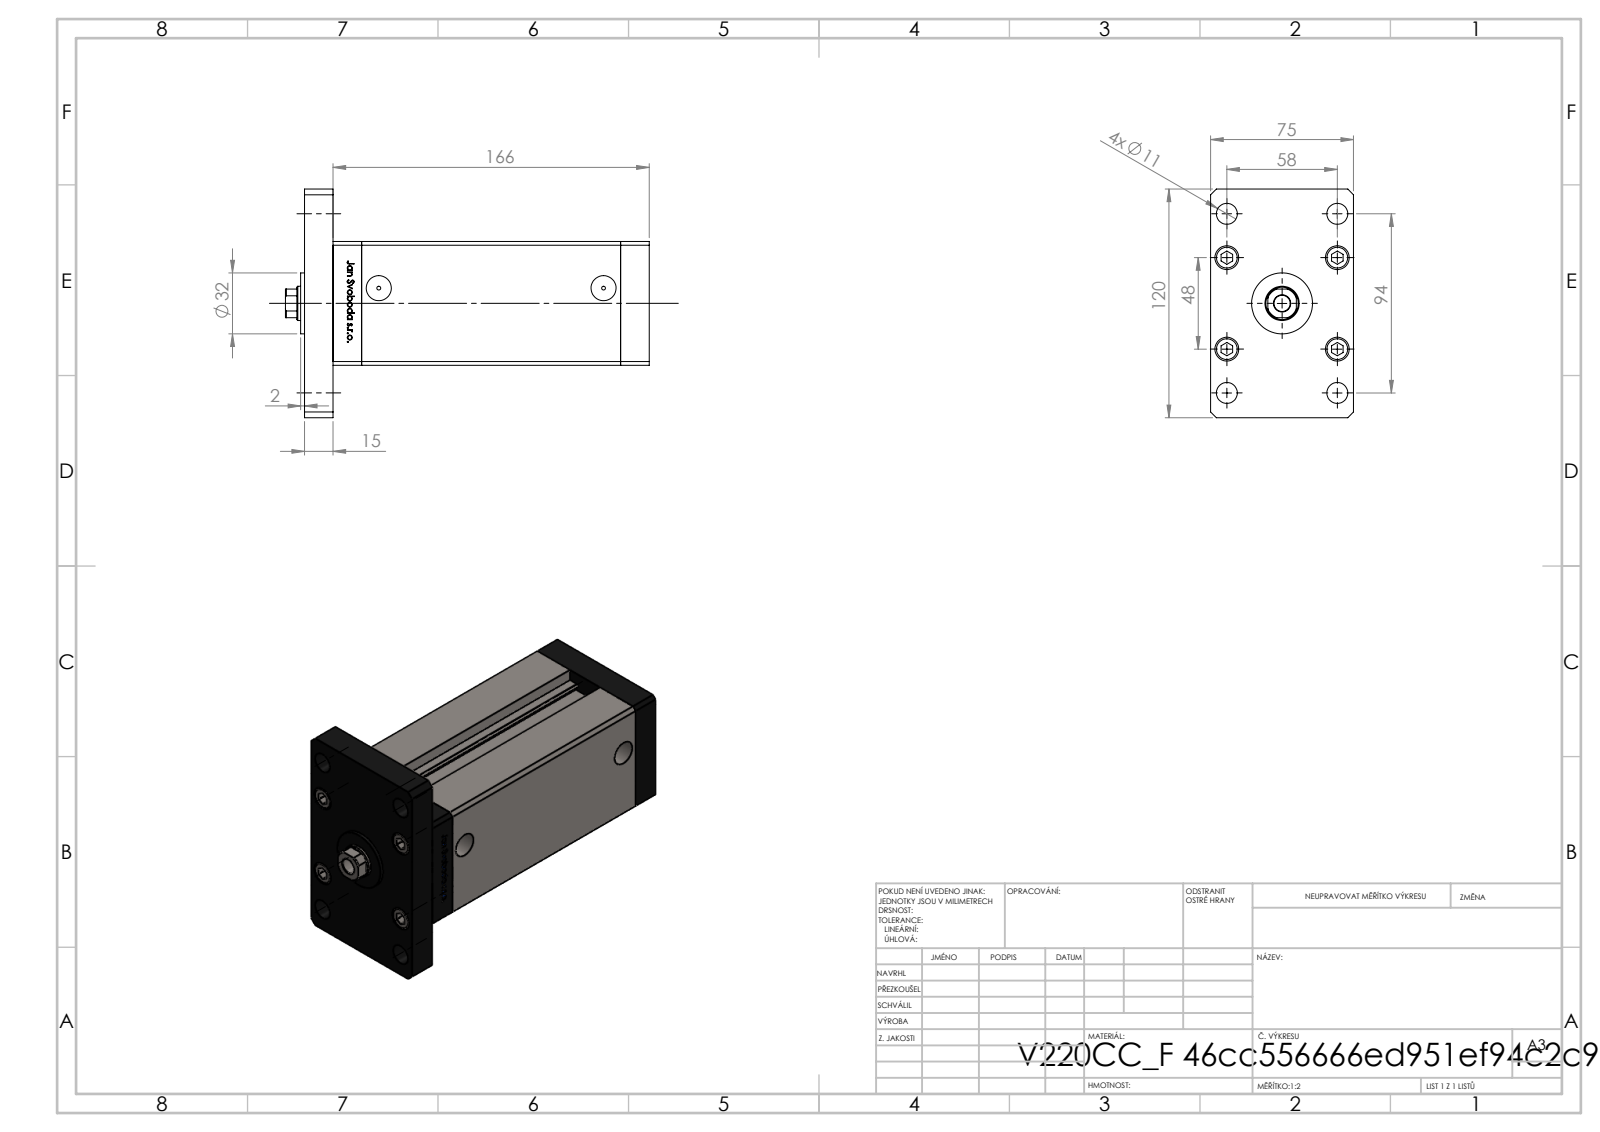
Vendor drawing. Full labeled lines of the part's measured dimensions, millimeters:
Part name (STEP PRODUCT): V220C_VC_F; V220C_F; V220C BACK_F; V220C_F_MIDDLE (+2 more)
STEP written by: SolidWorks 2019 (CONFIG_CONTROL_DESIGN)
Units: millimetres
Bodies: 19 solids, 1308 faces (515 planar, 187 cylindrical, 606 other)
Overall size (bounding box): 191 × 120 × 75
Volume: 848 554 mm³ · Surface area: 159 946 mm²
Round holes (diameter × count): ⌀9 ×5, ⌀13.5 ×5, ⌀8 ×4, ⌀11 ×4, ⌀12.5 ×4, ⌀2 ×2, ⌀13.16 ×2, ⌀8.5 ×1, ⌀18 ×1, ⌀19.5 ×1
Round bosses / shafts (diameter × count): ⌀12.5 ×5, ⌀8 ×5, ⌀32 ×1
Partial cylindrical surfaces — rounded edges, fillets, slot ends (radius × count): R0.93 ×2, R8.5 ×1
Main face-to-face distances: 15, 75, 151, 166, 65, 30, 136, 181, 13, 153
Hole centre spacings: 24, 23, 37.64, 55.23, 58, 62.39, 71, 91.68
